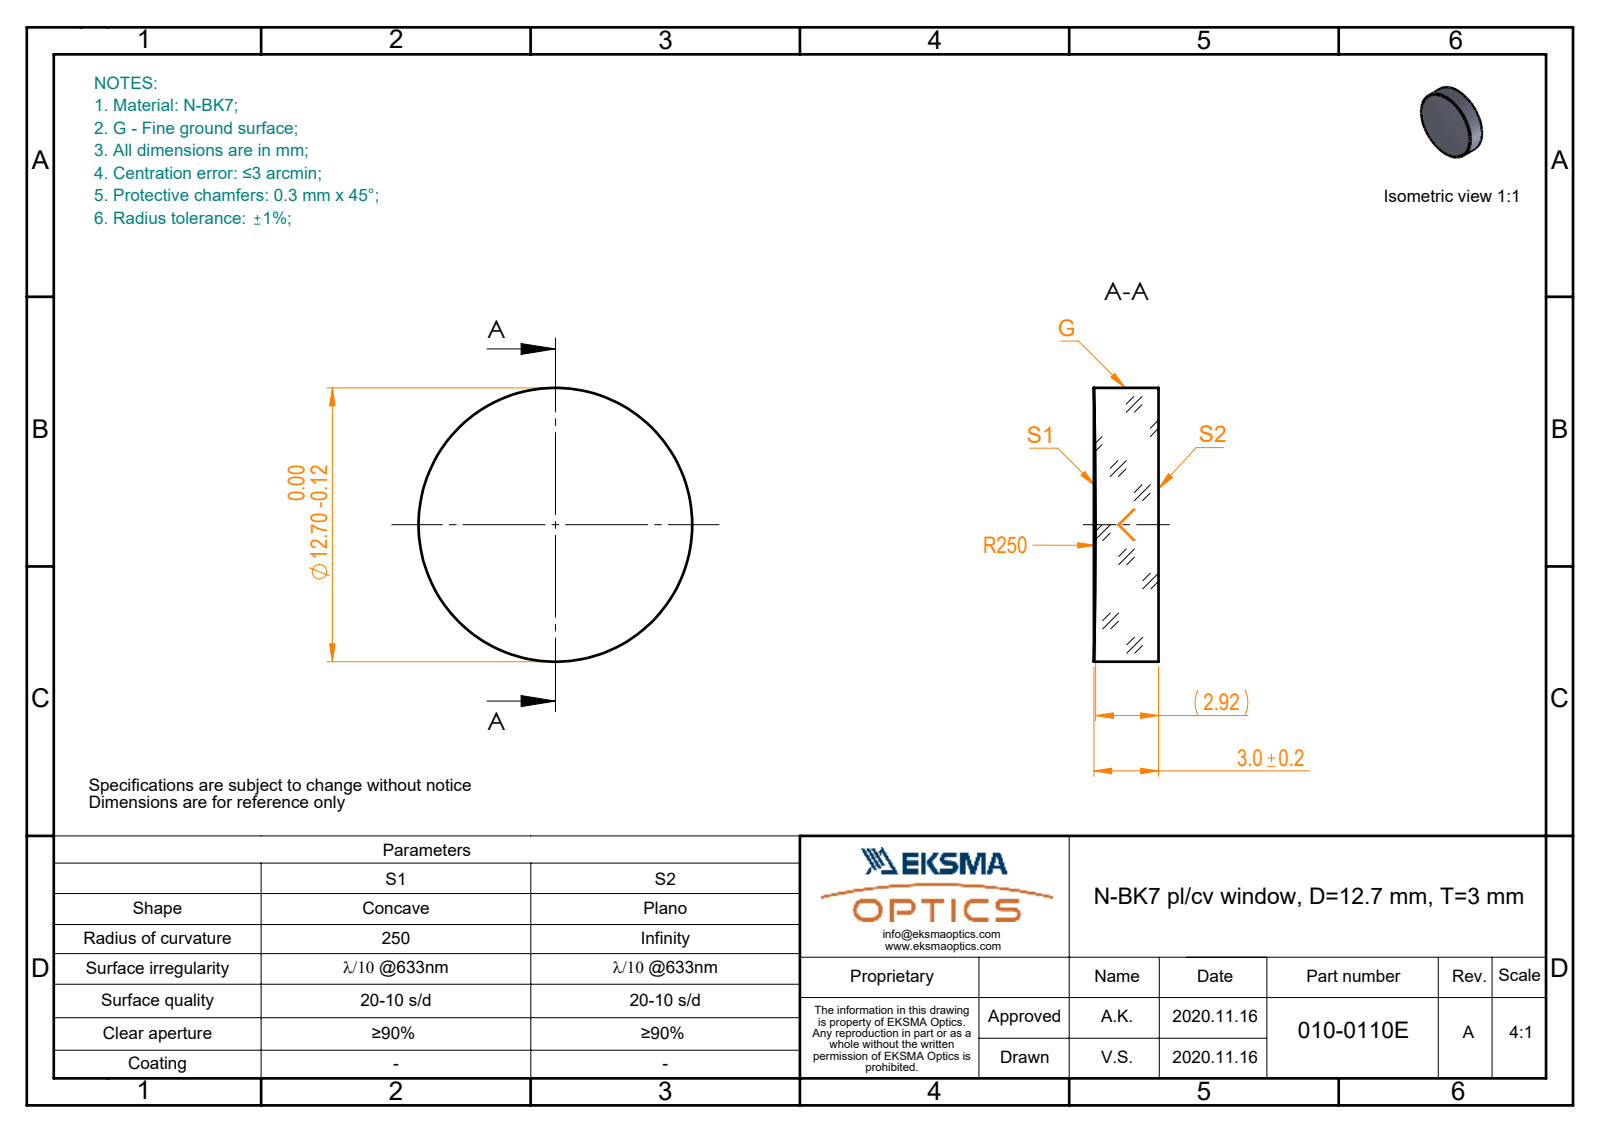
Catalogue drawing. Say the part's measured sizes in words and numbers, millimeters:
The part is named "010-0110E_N-BK7_PCV_window". Its 3-D file was written by "SolidWorks 2019 (CONFIG_CONTROL_DESIGN)". It is 1 solid with 5 faces: 1 planar, 2 cylindrical and 2 other. Overall it measures 12.7 by 12.7 by 3 millimeters. Its volume is 375 cubic millimeters and its surface area 373 square millimeters. Round bosses or shafts: 1 of diameter 12.7.
